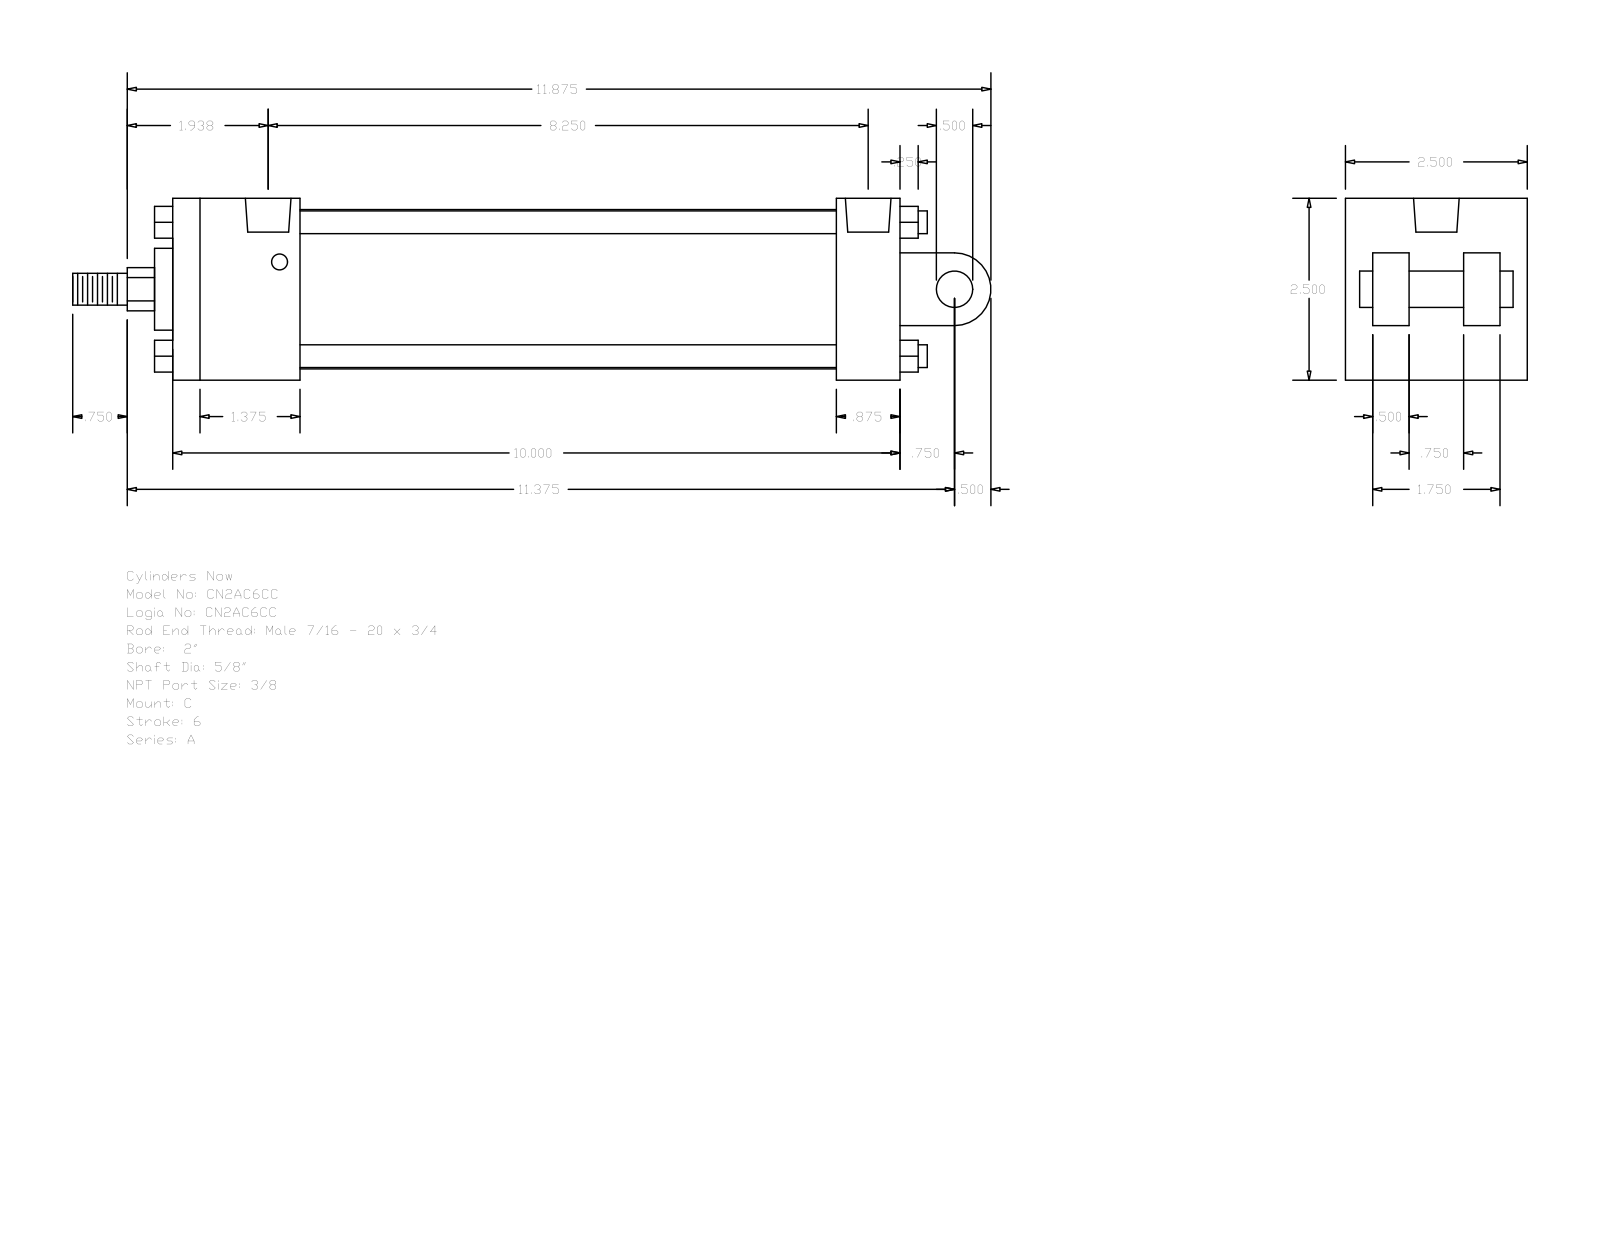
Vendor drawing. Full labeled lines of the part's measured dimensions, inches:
Part name (STEP PRODUCT): A_C__0200_0.625
STEP written by: GSSL Pune (CONFIG_CONTROL_DESIGN)
Units: inches
Bodies: 0 solids, 135 faces (102 planar, 33 cylindrical, 0 other)
Overall size (bounding box): 12.625 × 2.5 × 2.5
Round holes (diameter × count): ⌀0.219 ×4, ⌀0.627 ×2
Round bosses / shafts (diameter × count): ⌀0.313 ×4, ⌀2.19 ×1, ⌀1.125 ×1, ⌀0.625 ×1, ⌀0.5 ×1, ⌀0.437 ×1
Partial cylindrical surfaces — rounded edges, fillets, slot ends (radius × count): R0.297 ×1, R0.5 ×1
Main face-to-face distances: 2.5, 10, 1.75, 0.375, 8.25, 9.125, 7.375, 0.875, 0.5, 0.25
Hole centre spacings: 7.937, 0.156, 0.157, 8.093, 8.094, 8.25
